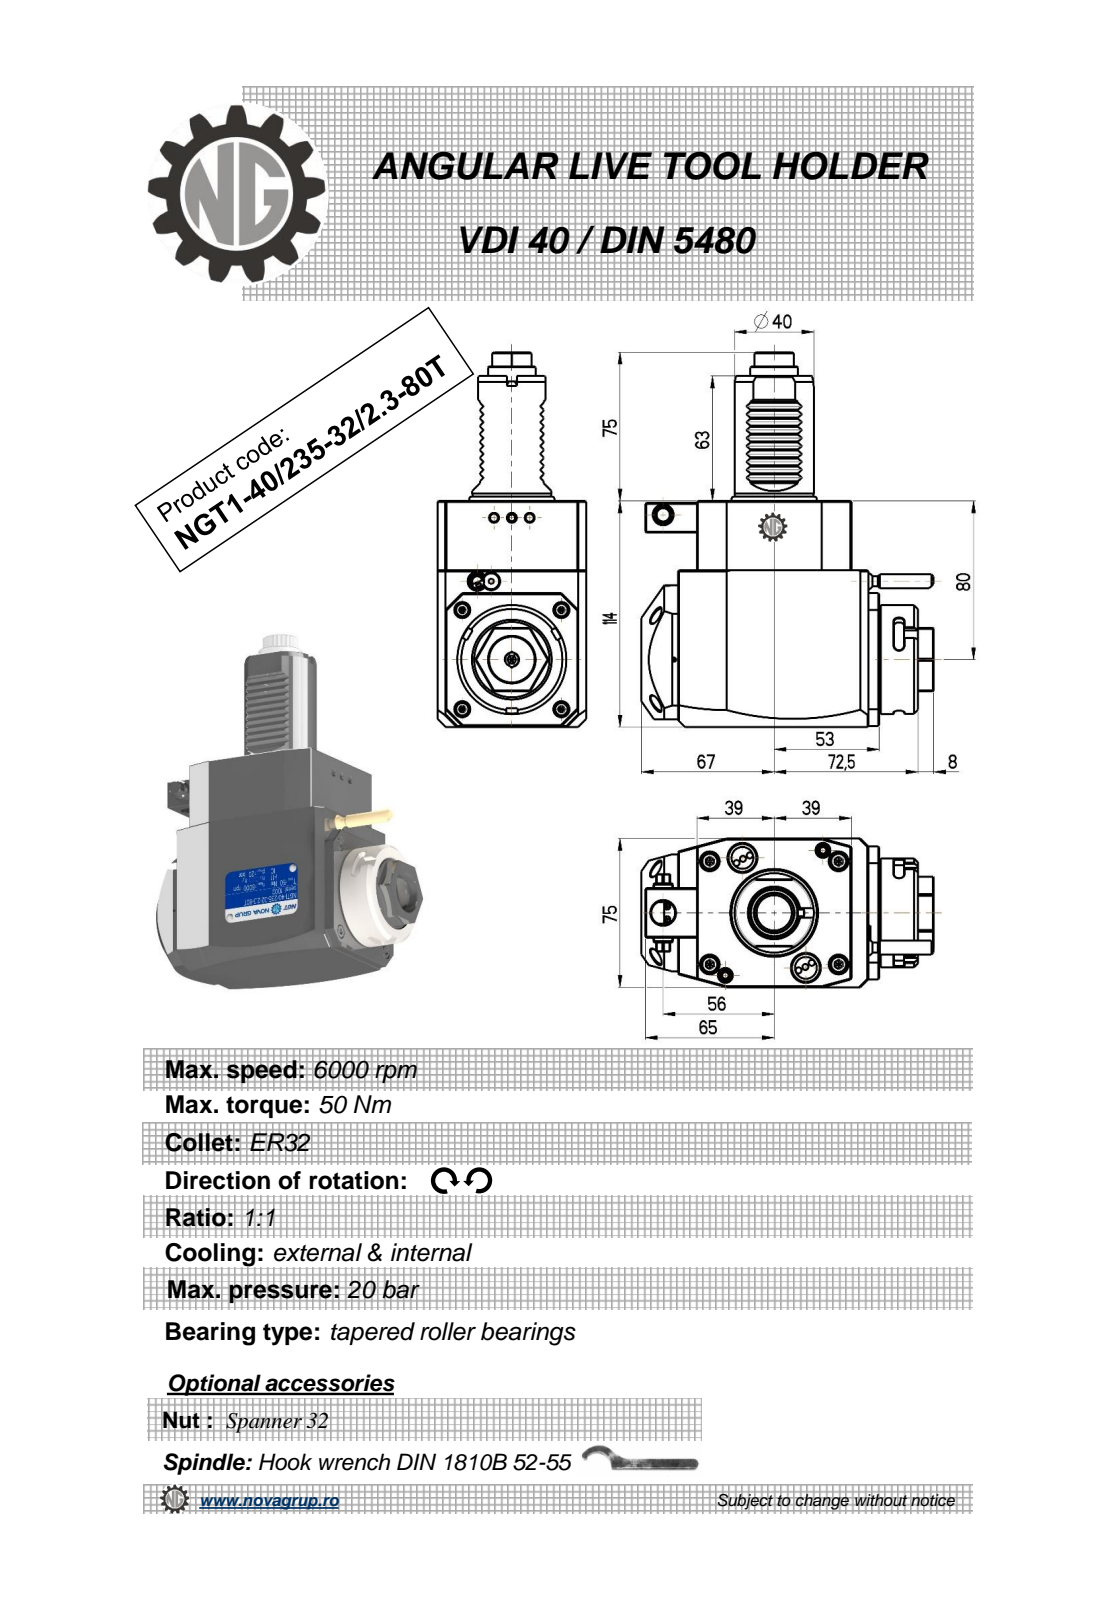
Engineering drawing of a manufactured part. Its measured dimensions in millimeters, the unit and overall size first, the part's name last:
Units: millimetres
Overall size (bounding box): 189 × 147.5 × 75
Round holes (diameter × count): ⌀2.5 ×1, ⌀3 ×1, ⌀9.5 ×1, ⌀12 ×1, ⌀23 ×1
Round bosses / shafts (diameter × count): ⌀8 ×2, ⌀55 ×1, ⌀48 ×1, ⌀40 ×1, ⌀24 ×1, ⌀10 ×1, ⌀7 ×1, ⌀5 ×1
Partial cylindrical surfaces — rounded edges, fillets, slot ends (radius × count): R2.08 ×48, R0.3 ×20, R2.5 ×6, R180 ×2, R3.85 ×1, R4.25 ×1, R9.08 ×1, R9.92 ×1
Main face-to-face distances: 75, 114, 14, 78, 92, 79, 25, 19.5, 111.5, 33.5
Hole centre spacings: 36.47, 43.2, 71.5
Volume: 961 518 mm³ · Surface area: 72 300 mm²
Bodies: 1 solid, 508 faces (228 planar, 182 cylindrical, 98 other)
Part name (STEP PRODUCT): NGT1_40_235_32_1_3_80T
STEP written by: PRO/ENGINEER BY PARAMETRIC TECHNOLOGY CORPORATION, 2010280 (CONFIG_CONTROL_DESIGN)
